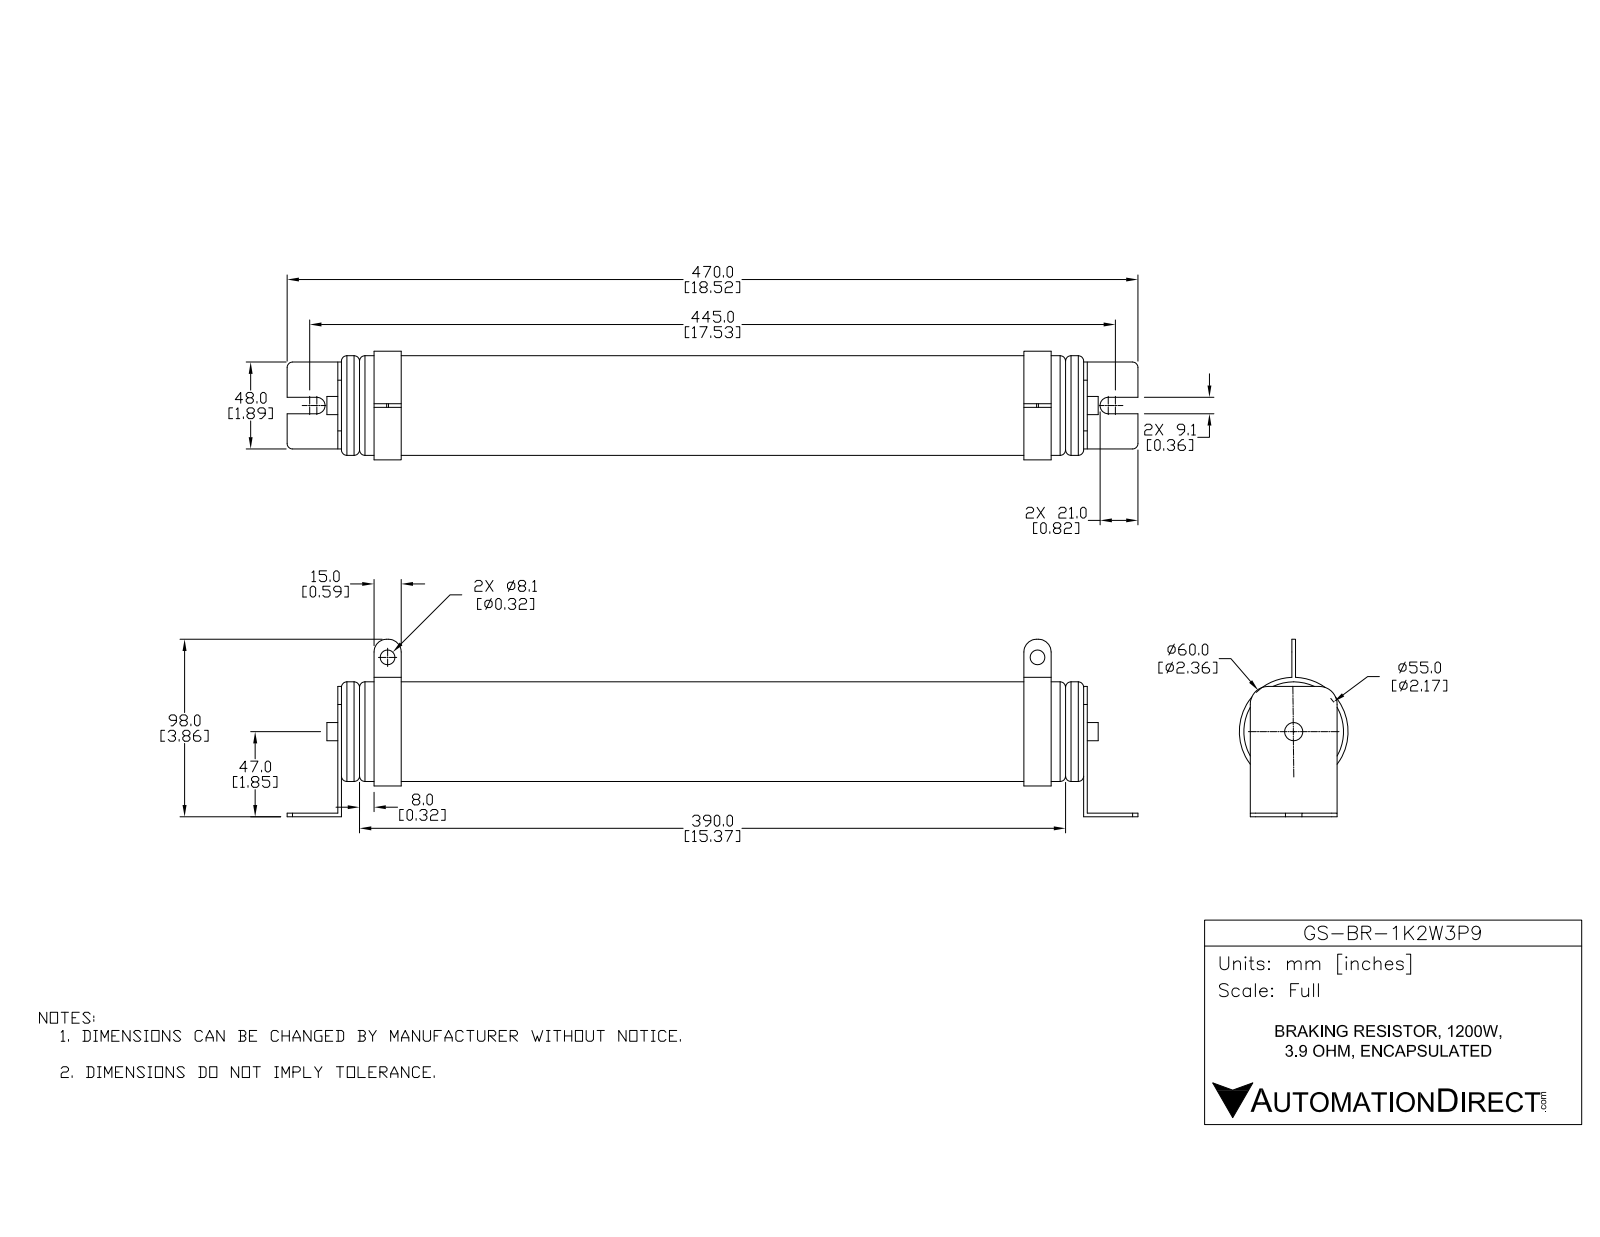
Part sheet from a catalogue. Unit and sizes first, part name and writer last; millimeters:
Units: millimetres
Overall size (bounding box): 470 × 98 × 60
Round holes (diameter × count): ⌀8.1 ×2
Round bosses / shafts (diameter × count): ⌀60 ×1, ⌀55 ×1, ⌀55 ×1, ⌀10 ×1
Partial cylindrical surfaces — rounded edges, fillets, slot ends (radius × count): R3 ×4, R7 ×4, R4.5 ×2, R10 ×2
Main face-to-face distances: 2, 414, 412, 410, 35, 379, 33, 377, 20, 394
Hole centre spacings: 359
Volume: 1 006 000 mm³ · Surface area: 92 390 mm²
Bodies: 2 solids, 91 faces (41 planar, 38 cylindrical, 12 other)
Part name (STEP PRODUCT): GS-BR-1K2W3P9
STEP written by: SolidWorks 2015 (AUTOMOTIVE_DESIGN)
